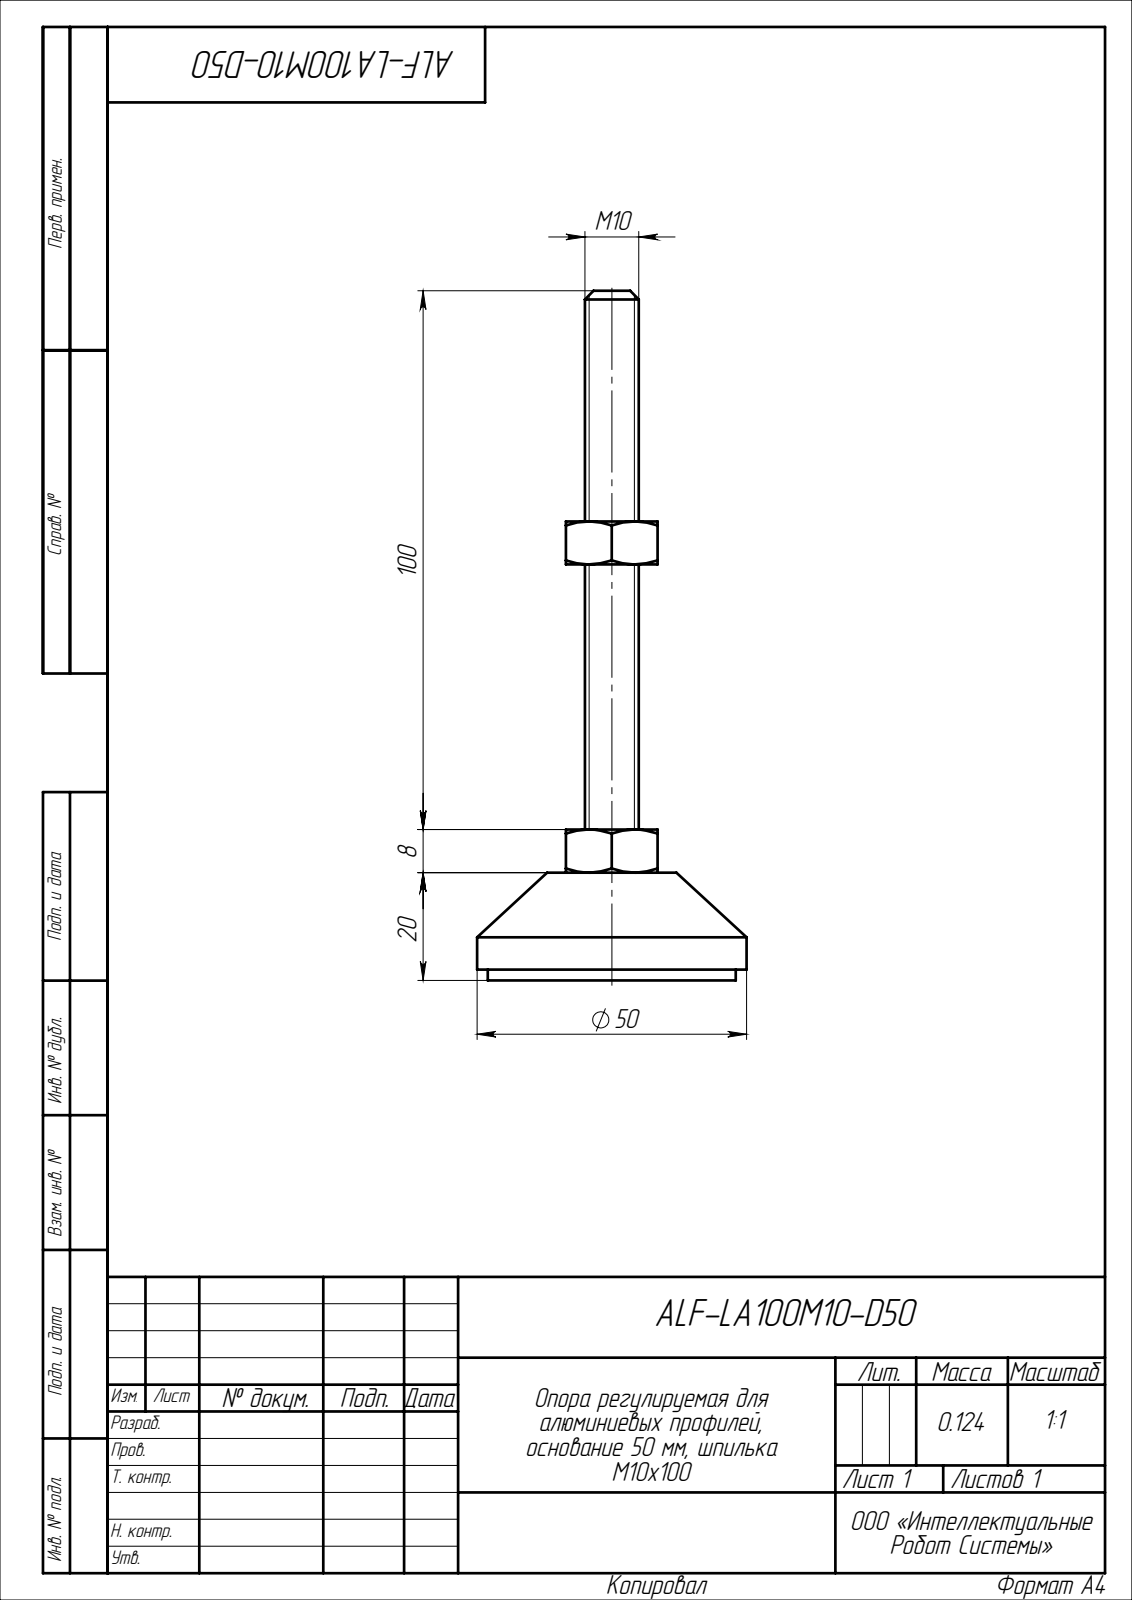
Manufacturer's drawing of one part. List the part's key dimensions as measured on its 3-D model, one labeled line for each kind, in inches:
Part name (STEP PRODUCT): ALF-LA100M10-D50
STEP written by: SolidWorks 2022 (CONFIG_CONTROL_DESIGN)
Units: inches
Bodies: 1 solid, 55 faces (19 planar, 8 cylindrical, 28 other)
Overall size (bounding box): 5.039 × 1.969 × 1.969
Volume: 2.423 in³ · Surface area: 15.26 in²
Round bosses / shafts (diameter × count): ⌀1.969 ×1, ⌀1.811 ×1, ⌀0.394 ×1
Main face-to-face distances: 0.669, 0.079, 0.315, 2.252, 0.787, 0.709, 1.102, 1.024, 3.039, 3.354
